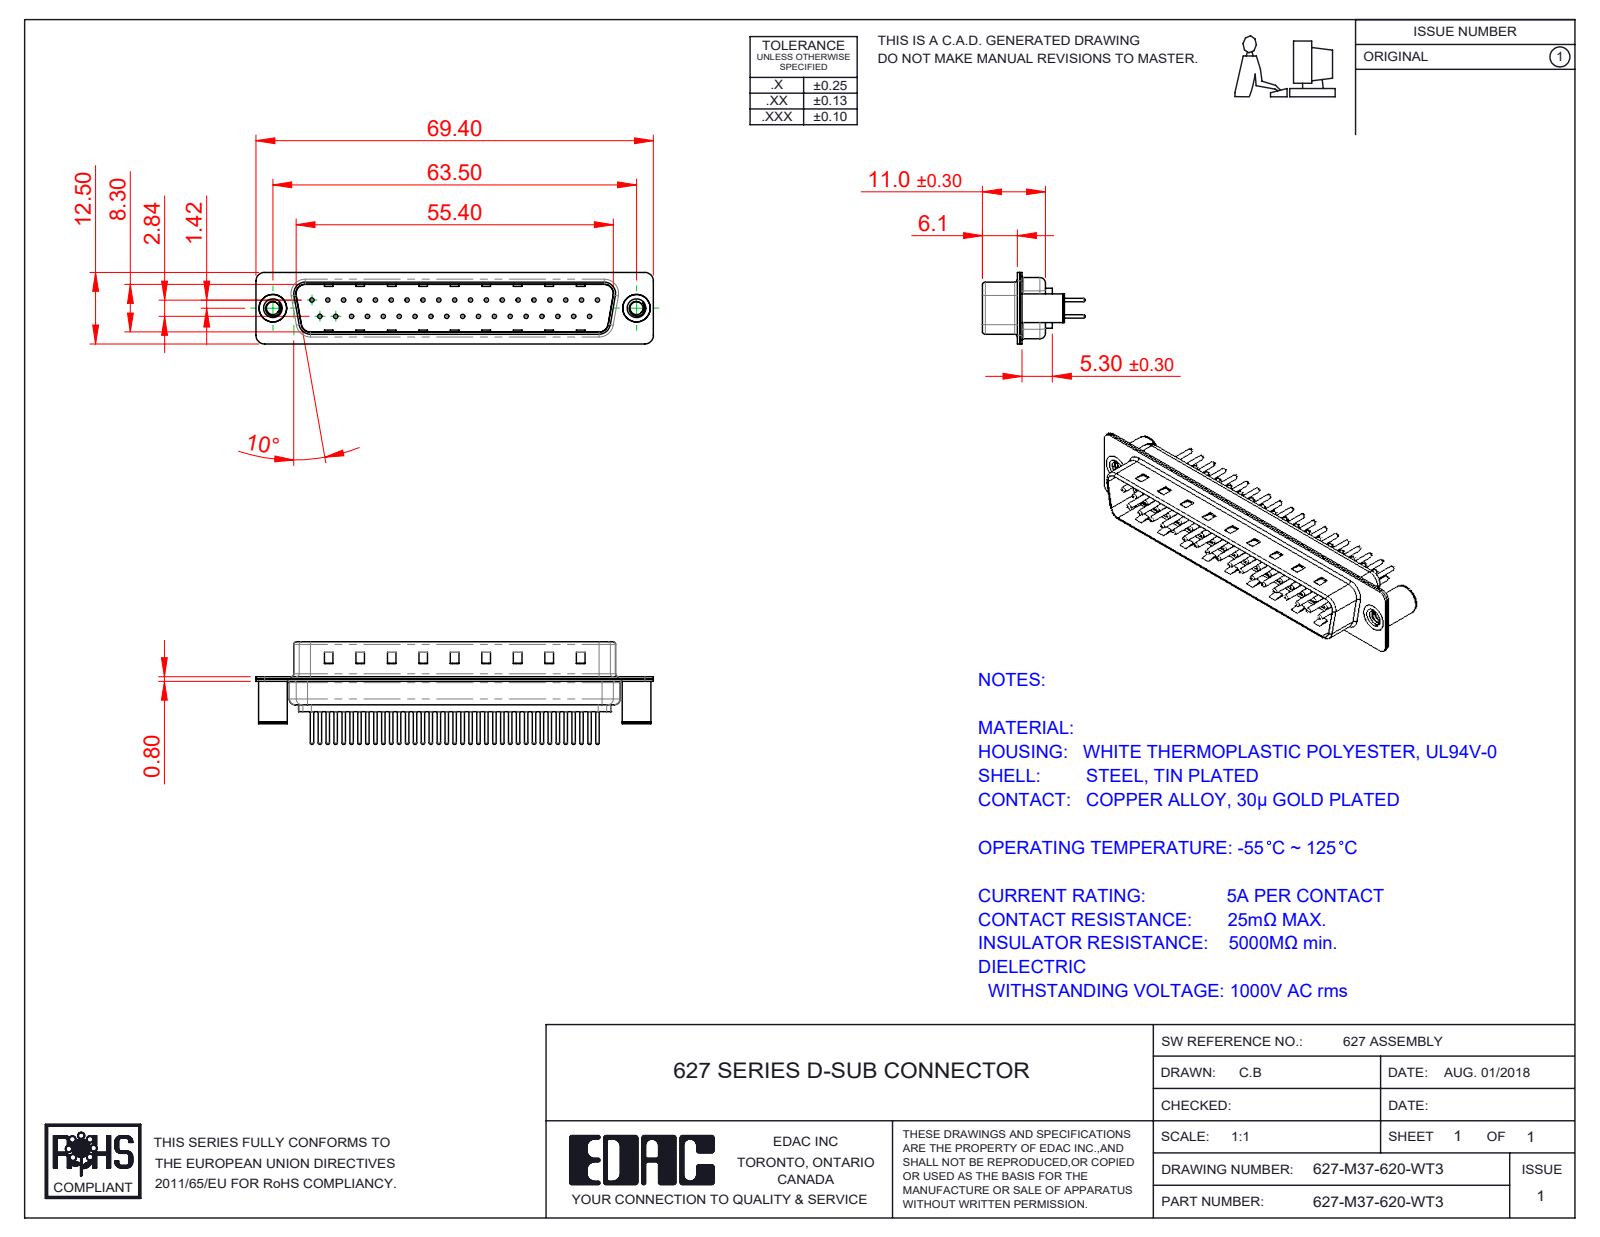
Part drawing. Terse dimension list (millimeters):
name: 627M Housing_37 Contacts; 627-M37-620-WT3; 627M Shell Rear_37 Contacts; 627M Shell Front_37 Contacts (+3 more)
written by: SolidWorks 2020 (CONFIG_CONTROL_DESIGN)
unit: mm
bodies: 42 solids, 1815 faces (462 planar, 683 cylindrical, 670 other)
size: 69.4 × 17.9 × 12.5
volume: 3 891 mm³; area: 9 528 mm²
holes: 37× ⌀0.75, 37× ⌀1.6, 37× ⌀2, 2× ⌀2.26, 2× ⌀3.26, 2× ⌀4, 2× ⌀4.8
bosses: 37× ⌀1.5, 37× ⌀0.6, 2× ⌀5, 2× ⌀4.9
rounds: 16× R1.5, 12× R2, 8× R0.5, 8× R1.6, 4× R0.25, 4× R0.6, 4× R0.65, 4× R0.9
face distances: 0.4, 0.8, 9.5, 9.1, 8.7, 9.9, 1.2, 5.7, 0.75, 0.35
hole spacings: 2.77, 5.54, 3.16, 8.31, 11.08, 13.85, 16.62, 19.39
